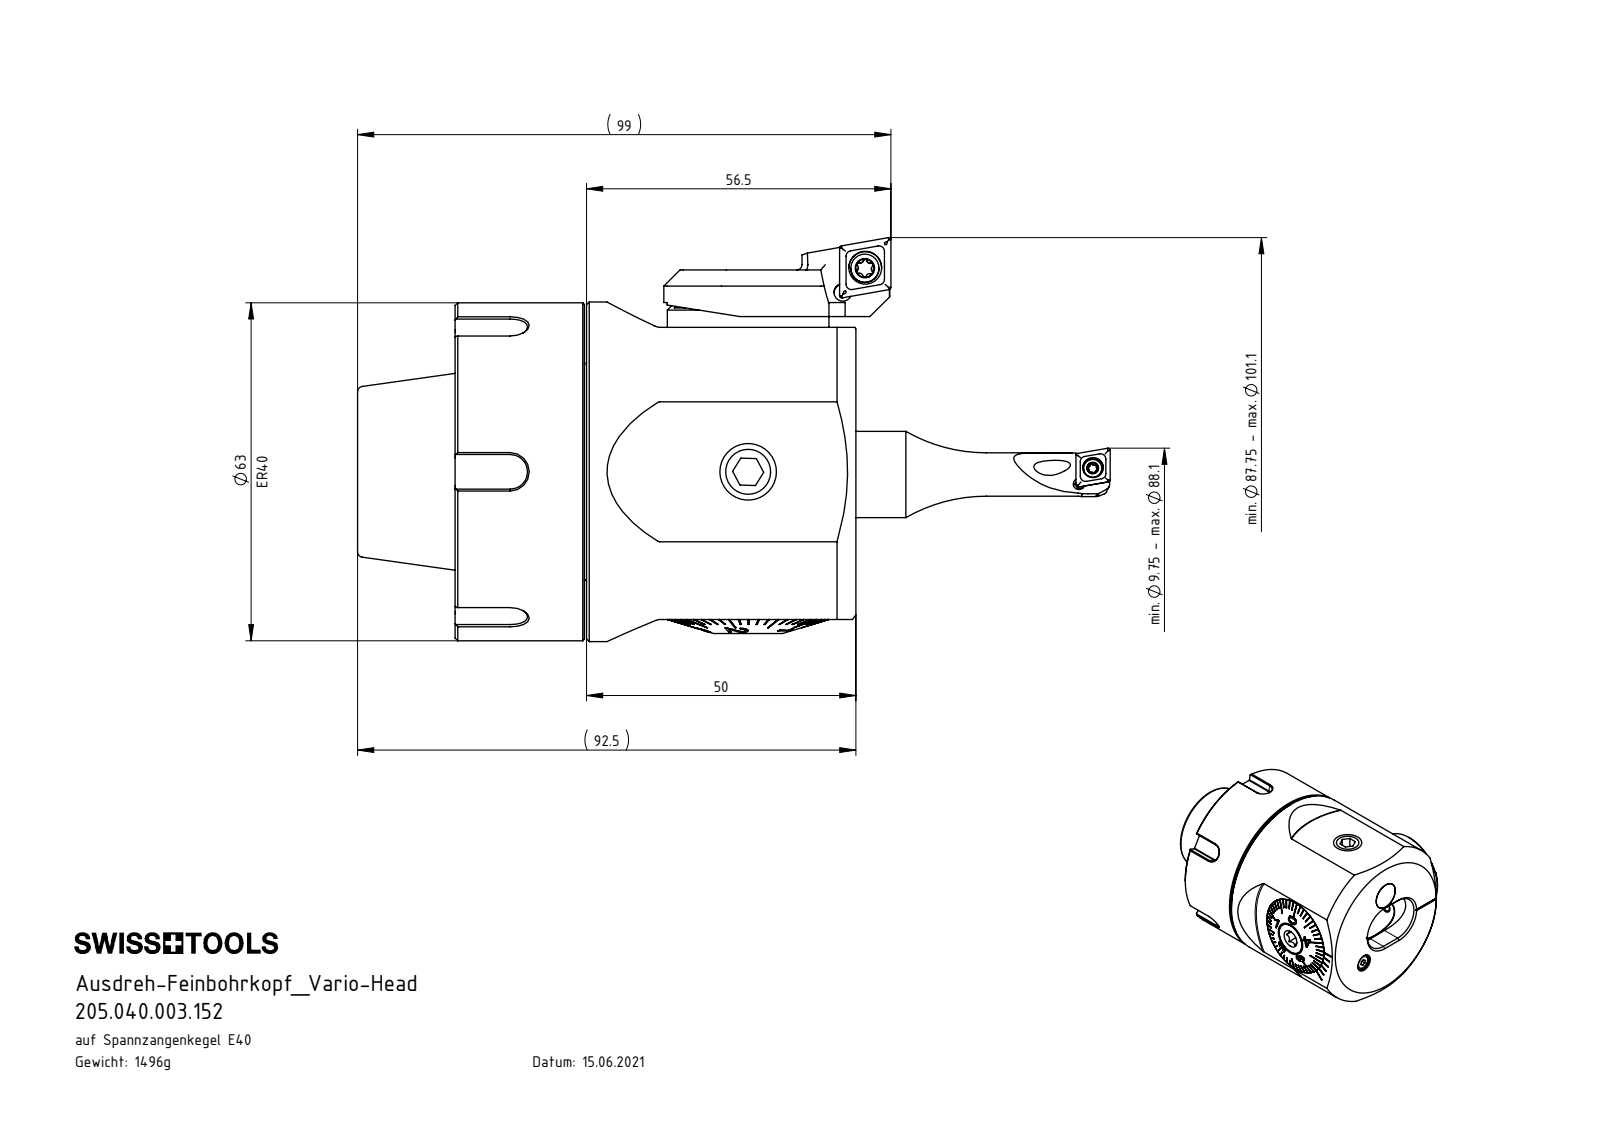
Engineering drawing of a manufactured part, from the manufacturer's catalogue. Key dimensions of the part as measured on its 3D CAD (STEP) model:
Part name (STEP PRODUCT): DIN 7984 - M3 x 8_DIN 7984 - M3 x 5; Sprengring_15.07.2011_003_Sprengring 40; A55-BG3.011.033_A_gekrzt; AV6-BG2.014.011_B_Abgedreht (+8 more)
STEP written by: SolidWorks 2017 (AUTOMOTIVE_DESIGN)
Units: millimetres
Bodies: 16 solids, 676 faces (374 planar, 92 cylindrical, 210 other)
Overall size (bounding box): 92.5 × 64.76 × 63
Volume: 191 350 mm³ · Surface area: 59 919 mm²
Round holes (diameter × count): ⌀3.3 ×2, ⌀6 ×2, ⌀8.5 ×2, ⌀1 ×1, ⌀2.5 ×1, ⌀4.2 ×1, ⌀8 ×1, ⌀10 ×1, ⌀11.75 ×1, ⌀12 ×1, ⌀12.4 ×1, ⌀14 ×1
Round bosses / shafts (diameter × count): ⌀10 ×2, ⌀63 ×1, ⌀62.7 ×1, ⌀40 ×1, ⌀37.5 ×1, ⌀30 ×1, ⌀29.98 ×1, ⌀29.9 ×1
Partial cylindrical surfaces — rounded edges, fillets, slot ends (radius × count): R0.3 ×12, R0.5 ×4, R1.4 ×4, R1.9 ×4, R3.2 ×3, R8.5 ×3, R1.5 ×2, R1 ×1
Main face-to-face distances: 50, 0.4, 50.4, 24, 24.4, 74.4, 57.7, 2.7, 2.8, 2.5
Hole centre spacings: 1.66, 10.5, 14.5, 14.59, 15.33, 16.6, 27.25
